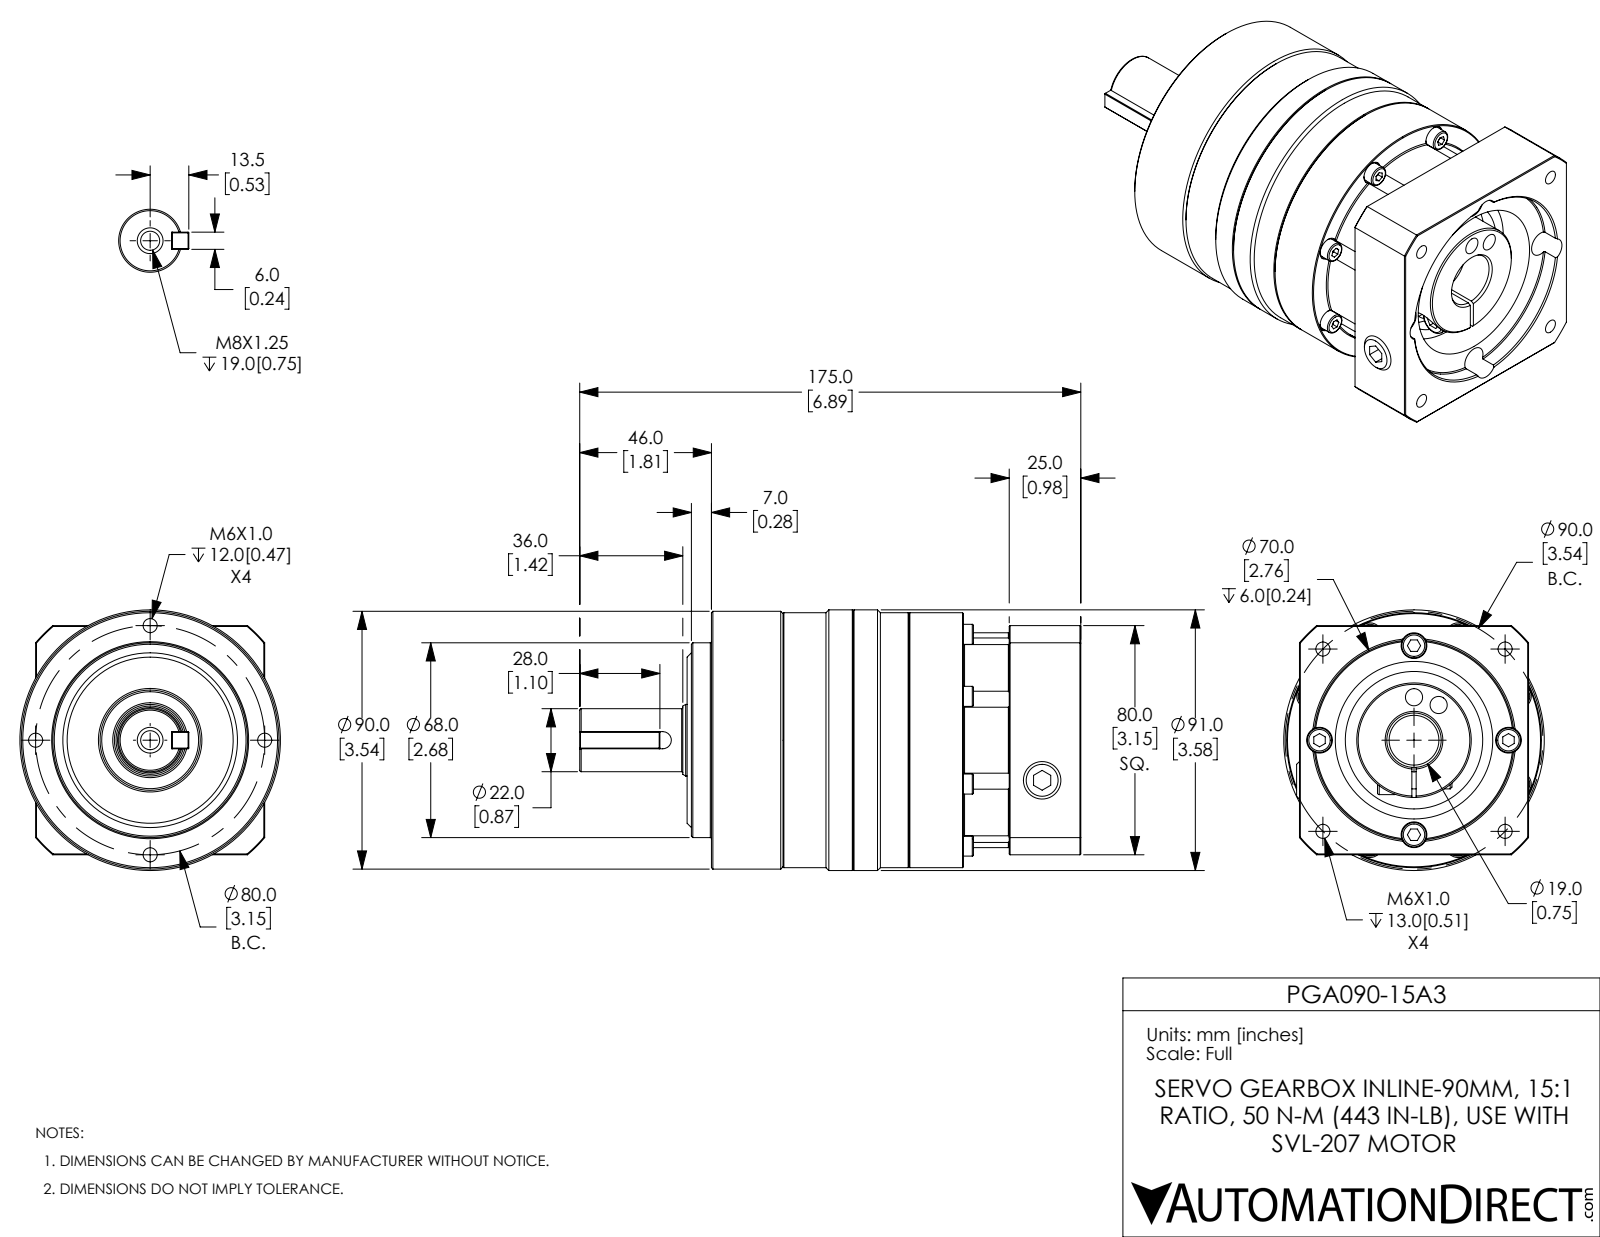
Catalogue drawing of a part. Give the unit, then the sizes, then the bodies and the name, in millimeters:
Units: millimetres
Overall size (bounding box): 175 × 91 × 91
Round holes (diameter × count): ⌀4.92 ×8, ⌀8 ×8, ⌀9 ×4, ⌀6 ×2, ⌀6.5 ×1, ⌀6.65 ×1, ⌀10.5 ×1, ⌀19 ×1, ⌀48 ×1, ⌀55 ×1, ⌀70 ×1
Round bosses / shafts (diameter × count): ⌀7 ×8, ⌀8.5 ×4, ⌀91 ×1, ⌀90 ×1, ⌀89 ×1, ⌀75 ×1, ⌀68 ×1, ⌀40 ×1
Partial cylindrical surfaces — rounded edges, fillets, slot ends (radius × count): R2.46 ×1, R3 ×1, R5.5 ×1, R52.5 ×1
Main face-to-face distances: 80, 129, 104, 25, 137.5, 8.5, 6, 112.5, 19, 16
Hole centre spacings: 15.61, 15.81, 17.29, 30.62, 31.84, 32.85, 40.01, 40.98
Volume: 765 993 mm³ · Surface area: 74 964 mm²
Bodies: 1 solid, 471 faces (179 planar, 126 cylindrical, 166 other)
Part name (STEP PRODUCT): PGA090-15A3
STEP written by: SolidWorks 2019 (CONFIG_CONTROL_DESIGN)
